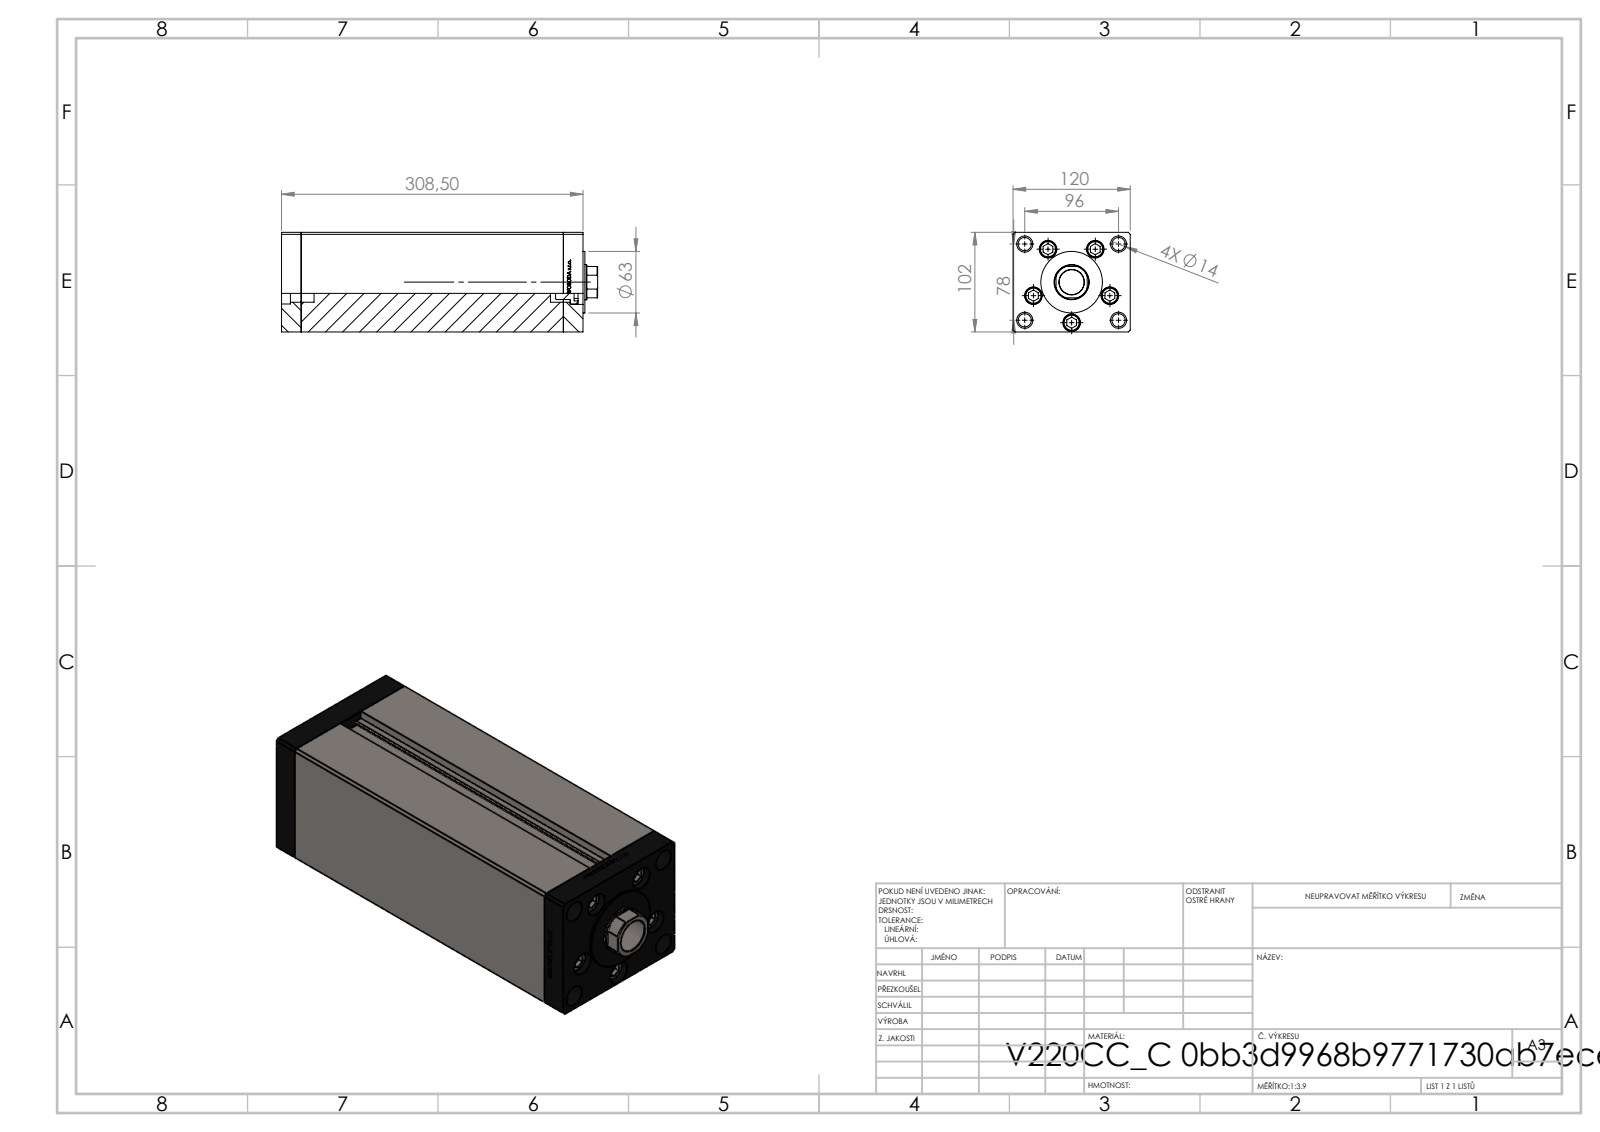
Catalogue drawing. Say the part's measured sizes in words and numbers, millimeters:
The part is named "V220C_C MIDDLE; V220C_VC_C; ALLEN BOLT; V220C BACK_C (+1 more)". Its 3-D file was written by "SolidWorks 2019 (CONFIG_CONTROL_DESIGN)". It is 13 solids with 1165 faces: 542 planar, 161 cylindrical and 462 other. Overall it measures 323.5 by 120 by 102 millimeters. Its volume is 3 135 000 cubic millimeters and its surface area 375 908 square millimeters. Round holes: 9 of diameter 13.5, 5 of diameter 18, 4 of diameter 12, 4 of diameter 16.5, 1 of diameter 17, 1 of diameter 25.5, 1 of diameter 36. Round bosses or shafts: 5 of diameter 8, 4 of diameter 17, 1 of diameter 63. Partial cylindrical surfaces (rounded edges, fillets, slot ends): 2 of radius 0.93, 1 of radius 17.5. The main face-to-face distances are 120, 102, 20, 268.5, 288.5, 34.25, 308.5, 274.25, 254.25, 14.25. The hole center spacings are 41.5, 61.85, 24.39, 26.69, 47.92, 48.07, 49.84, 53.57.
